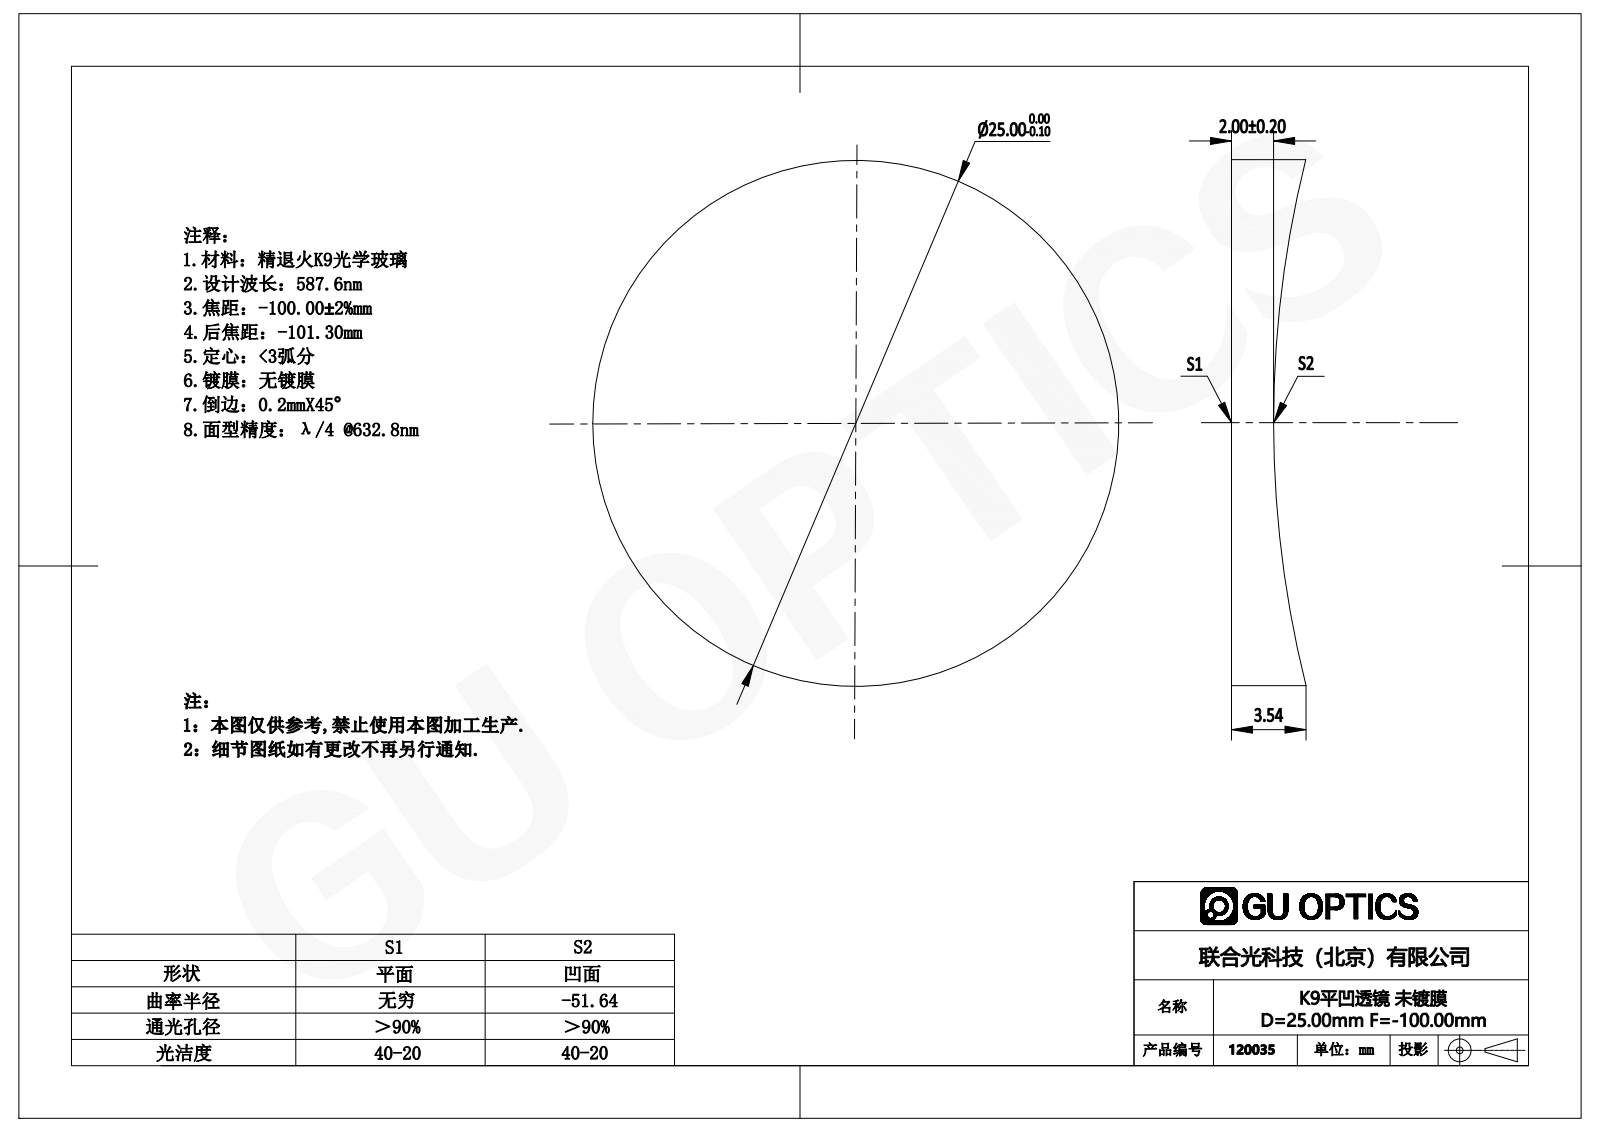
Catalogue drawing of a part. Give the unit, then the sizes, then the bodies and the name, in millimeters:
Units: millimetres
Overall size (bounding box): 25 × 25 × 3.53
Round bosses / shafts (diameter × count): ⌀25 ×1
Volume: 1 355 mm³ · Surface area: 1 266 mm²
Bodies: 1 solid, 5 faces (1 planar, 2 cylindrical, 2 other)
Part name (STEP PRODUCT): 120035
STEP written by: SolidWorks 2016 (AUTOMOTIVE_DESIGN)
